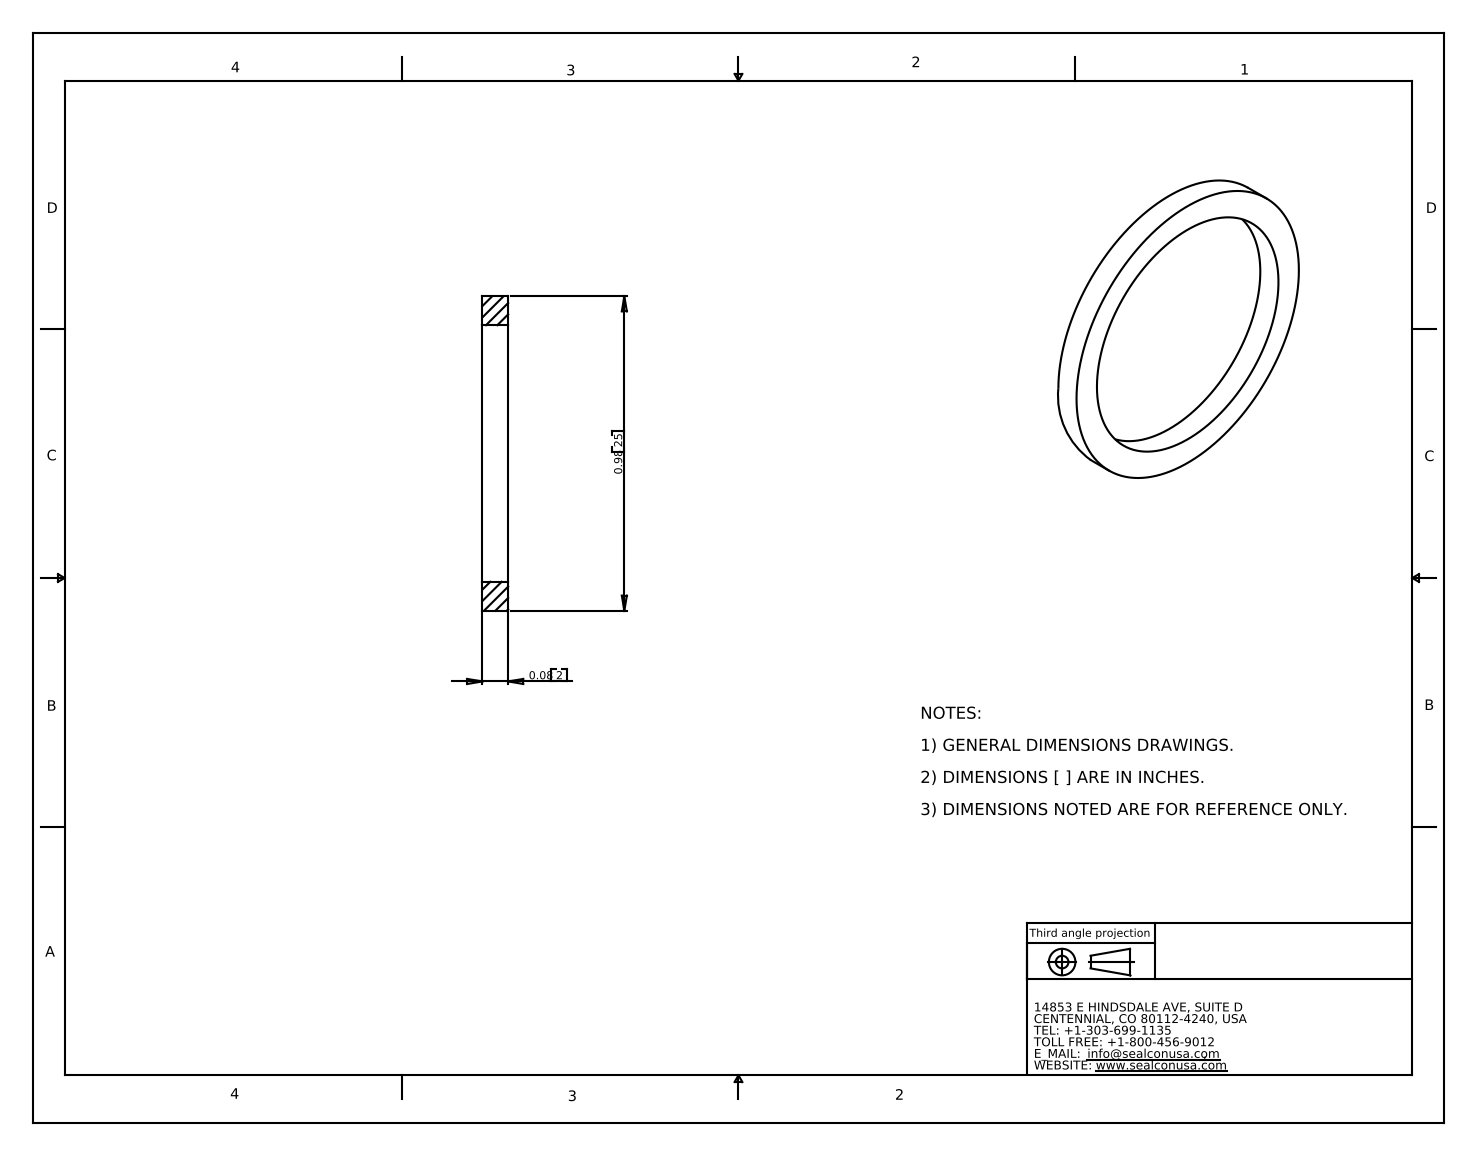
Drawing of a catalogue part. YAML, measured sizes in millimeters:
part_name: "SR-13-VT"
step_written_by: "SolidWorks 2007 (CONFIG_CONTROL_DESIGN)"
units: millimeters
bodies: {solids: 1, faces: 6, planar: 2, cylindrical: 4, other: 0}
overall_size: [24.9, 24.9, 2]
volume: 330
surface_area: 614
round_holes:
  - {diameter: 20.3, count: 1}
round_bosses_or_shafts:
  - {diameter: 24.9, count: 1}
face_to_face_distances: [2]
